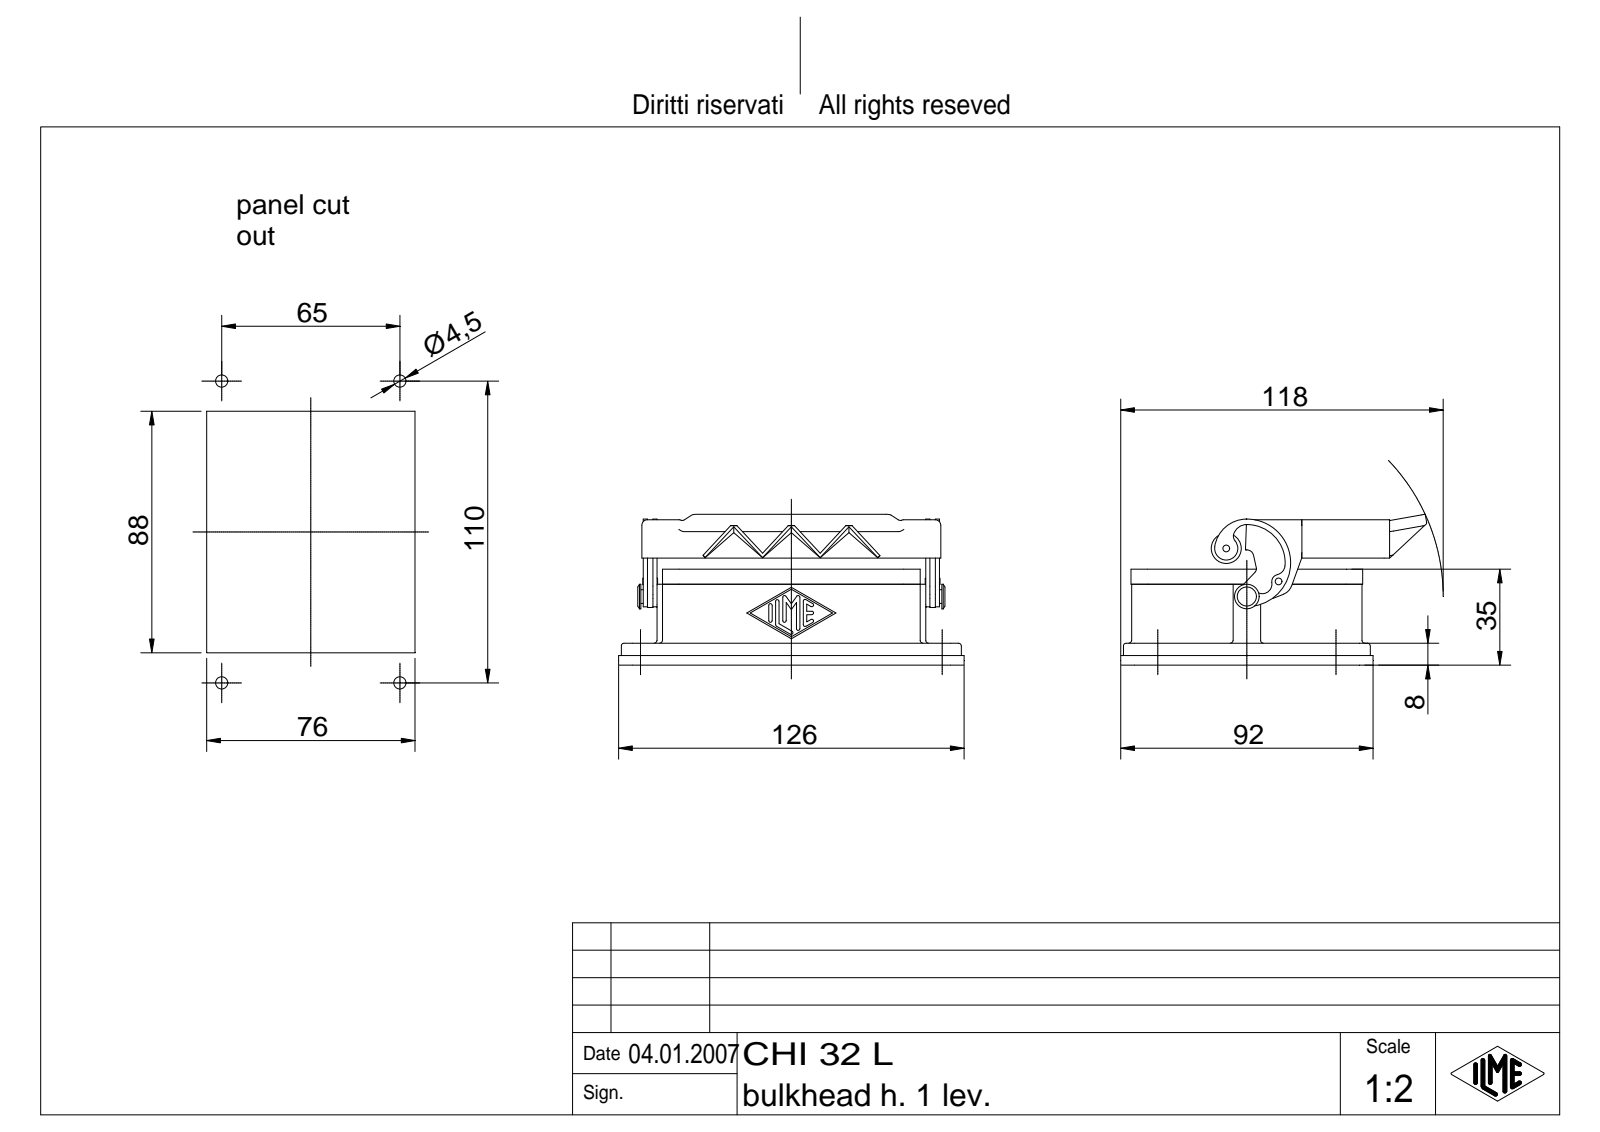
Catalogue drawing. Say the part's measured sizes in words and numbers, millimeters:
The part is named "CHI 32 L". Its 3-D file was written by "Autodesk Inventor 7 (AUTOMOTIVE_DESIGN)". It is 4 solids with 542 faces: 166 planar, 178 cylindrical and 198 other. Overall it measures 126 by 111.59 by 54.98 millimeters. Its volume is 91 823 cubic millimeters and its surface area 52 664 square millimeters. Round holes: 4 of diameter 4.4, 4 of diameter 4.5, 1 of diameter 2. Round bosses or shafts: 1 of diameter 11, 1 of diameter 9, 1 of diameter 5, 1 of diameter 3, 1 of diameter 2.5. Partial cylindrical surfaces (rounded edges, fillets, slot ends): 19 of radius 1, 14 of radius 0.62, 12 of radius 2, 8 of radius 6, 7 of radius 2.5, 6 of radius 5, 5 of radius 1.5, 5 of radius 4. The main face-to-face distances are 3, 91, 81, 8, 1, 88, 21.5, 4, 84, 29.5. The hole center spacings are 65, 110, 127.77.
